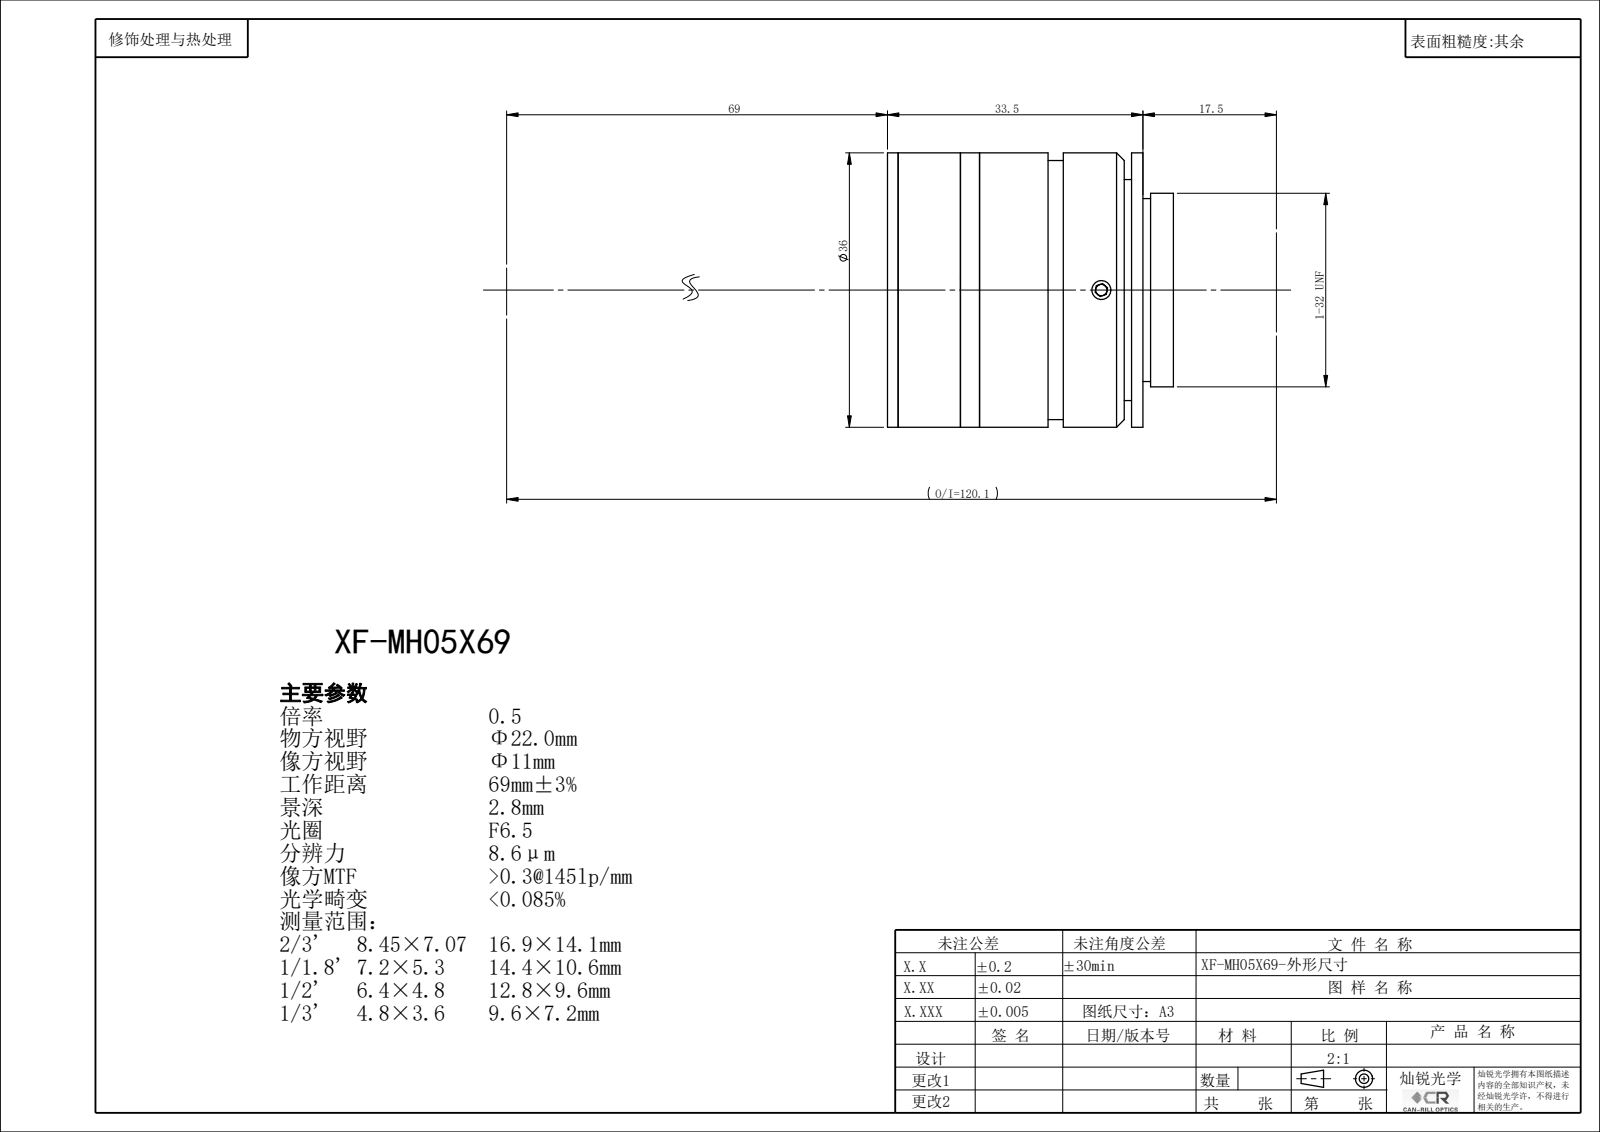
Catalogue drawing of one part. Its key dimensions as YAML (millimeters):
part_name: "XF-MH05X69"
step_written_by: "SolidWorks 2022 (CONFIG_CONTROL_DESIGN)"
units: millimeters
bodies: {solids: 0, faces: 93, planar: 45, cylindrical: 40, other: 8}
overall_size: [37.55, 36, 36]
round_holes:
  - {diameter: 2.5, count: 3}
  - {diameter: 9, count: 1}
  - {diameter: 13, count: 1}
  - {diameter: 17, count: 1}
  - {diameter: 20, count: 1}
  - {diameter: 21, count: 1}
  - {diameter: 21.5, count: 1}
  - {diameter: 24.9, count: 1}
  - {diameter: 26, count: 1}
round_bosses_or_shafts:
  - {diameter: 36, count: 1}
  - {diameter: 34, count: 1}
  - {diameter: 25.4, count: 1}
  - {diameter: 24, count: 1}
face_to_face_distances: [8.19, 10.69, 2.5, 32.15, 23.96, 21.46, 1.4, 9.59, 12.09, 33.55]
